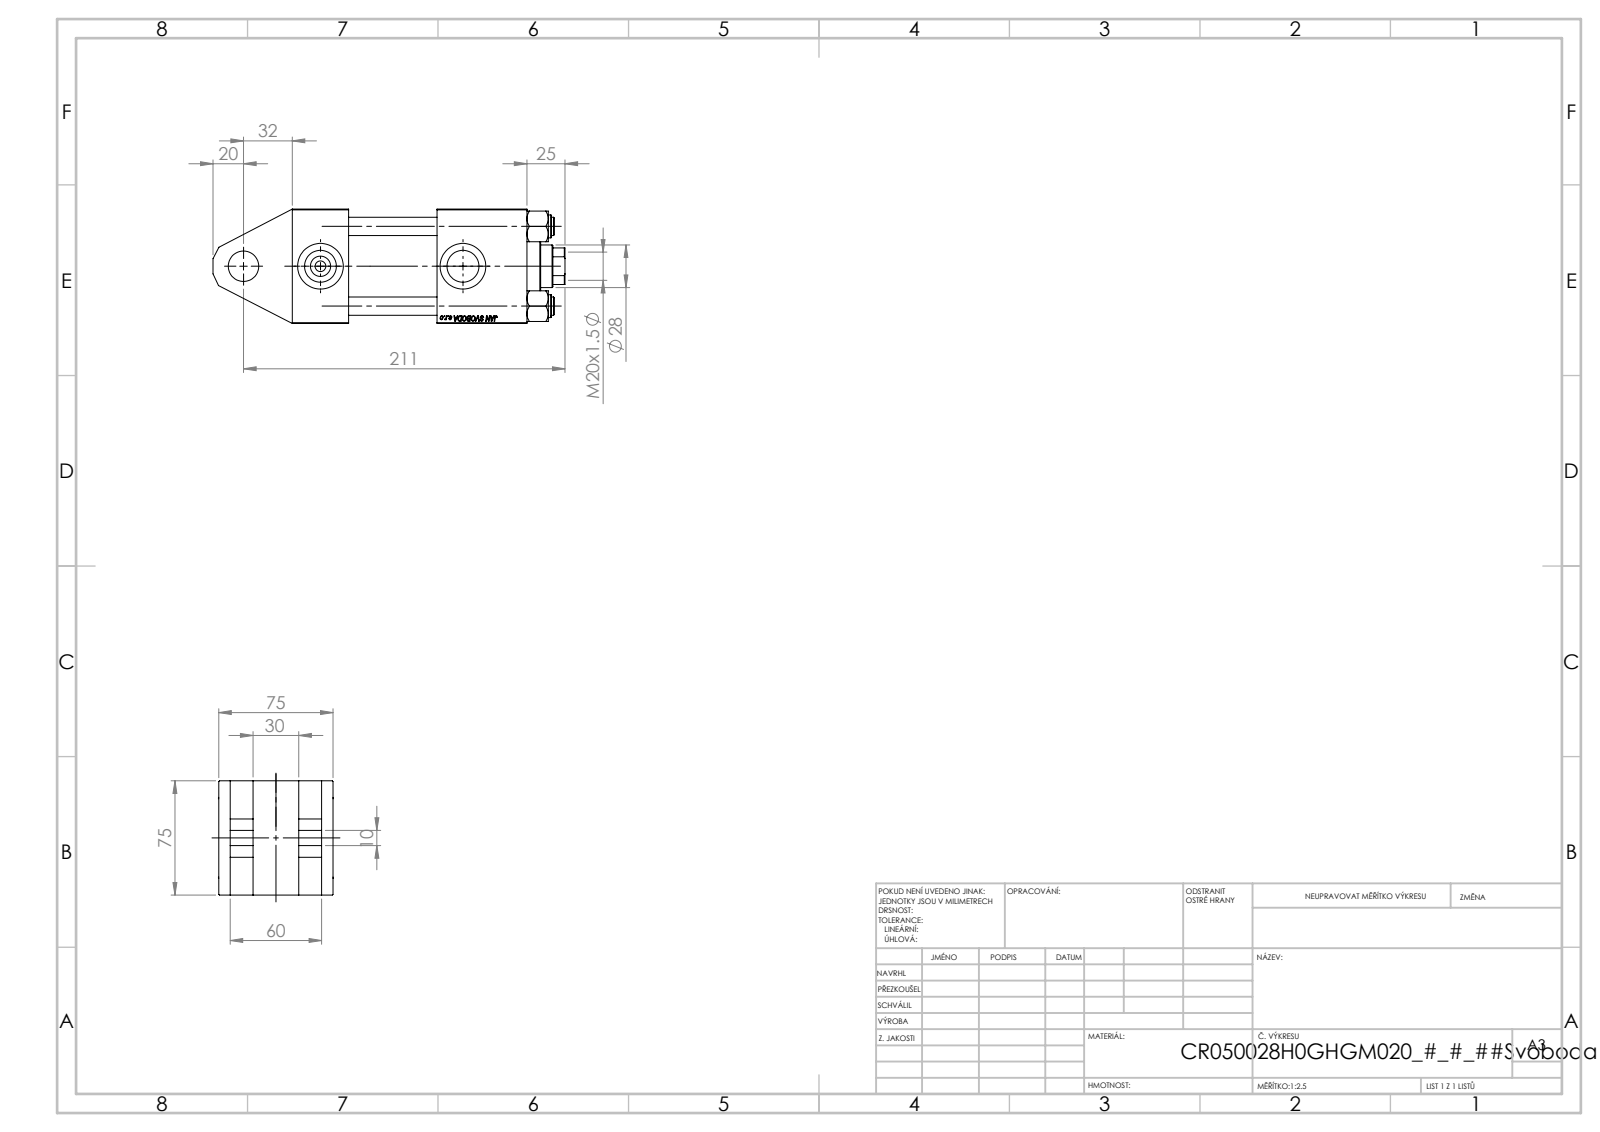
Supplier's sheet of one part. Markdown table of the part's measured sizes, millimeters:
| quantity | value |
| --- | --- |
| part name | V215CR_H_Body; V215CR_TYCINKA_H; NUT_M5_H; V215_VC_A (+1 more) |
| STEP written by | SolidWorks 2019 (CONFIG_CONTROL_DESIGN) |
| units | millimeters |
| bodies | 11 solids, 1129 faces (518 planar, 83 cylindrical, 528 other) |
| overall size | 231 × 75.54 × 75 |
| volume | 746 301 mm³ |
| surface area | 166 506 mm² |
| round holes (diameter × count) | 12 × 4, 7 × 2, 20.96 × 2, 30 × 2, 18.5 × 1, 20 × 1, 28 × 1, 31 × 1, 41 × 1, 50 × 1, 53 × 1 |
| round bosses / shafts (diameter × count) | 15 × 4, 56 × 1, 42 × 1 |
| partial cylindrical surfaces (radius × count) | 13.5 × 1 |
| main face-to-face distances | 75, 67.5, 7.5, 22.5, 52.5, 15, 45, 117, 95, 37 |
| hole center spacings | 36.98, 52.3, 73.96, 50.5, 93.5, 144 |
